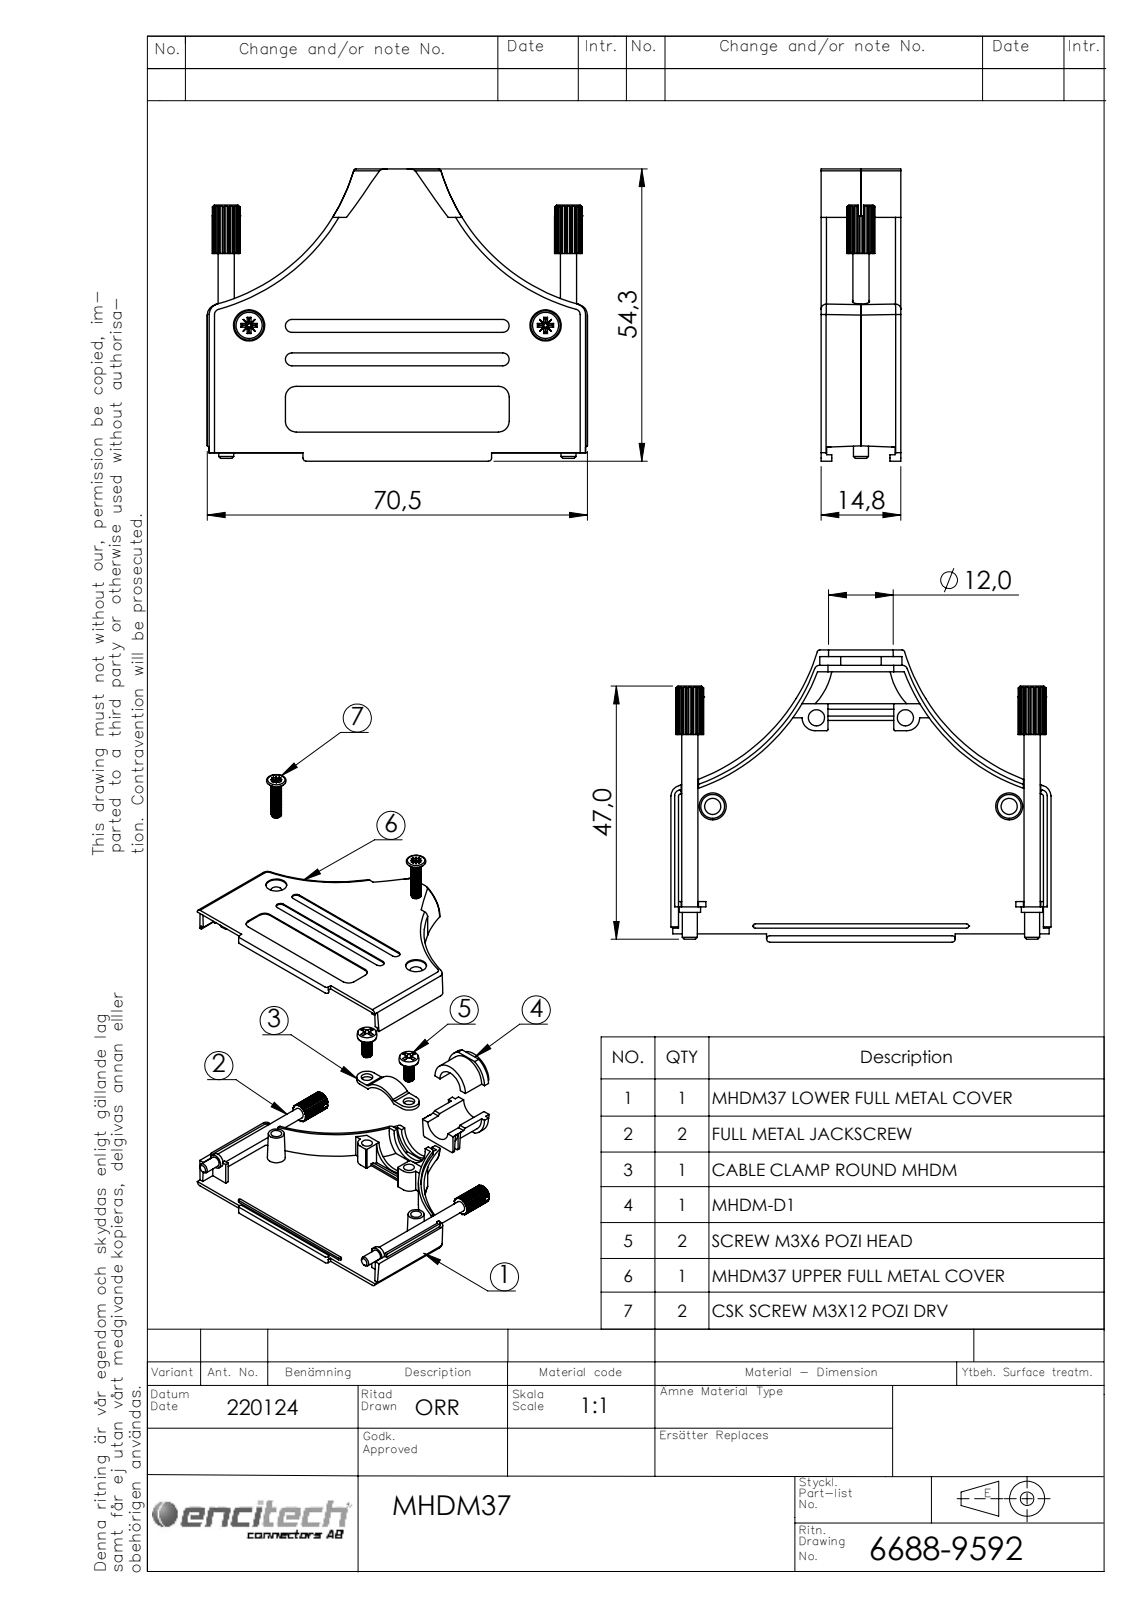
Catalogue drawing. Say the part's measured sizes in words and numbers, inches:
The part is named "6522-0122-03 (8mm SV); 6805-0136-04; 6855-0117-13; 6826-0141-02 (+5 more)". Its 3-D file was written by "SolidWorks 2021 (AUTOMOTIVE_DESIGN)". It is 11 solids with 835 faces: 407 planar, 324 cylindrical and 104 other. Overall it measures 2.776 by 2.138 by 0.583 inches. Its volume is 0.651 cubic inches and its surface area 31.17 square inches. Round holes: 4 of diameter 0.118, 4 of diameter 0.126, 2 of diameter 0.177, 2 of diameter 0.228, 1 of diameter 0.13, 1 of diameter 0.315, 1 of diameter 0.48. Round bosses or shafts: 4 of diameter 0.114, 2 of diameter 0.157, 2 of diameter 0.118, 2 of diameter 0.11, 1 of diameter 0.472. Partial cylindrical surfaces (rounded edges, fillets, slot ends): 14 of radius 0.039, 8 of radius 0.004, 7 of radius 1.445, 4 of radius 0.008, 4 of radius 0.02, 4 of radius 0.047, 4 of radius 0.079, 3 of radius 0.01. The main face-to-face distances are 0.541, 0.041, 0.5, 0.583, 0.03, 0.571, 0.53, 0.25, 0.28, 0.291. The hole center spacings are 0.997, 1.25, 1.549, 0.65, 2.165, 2.5.
